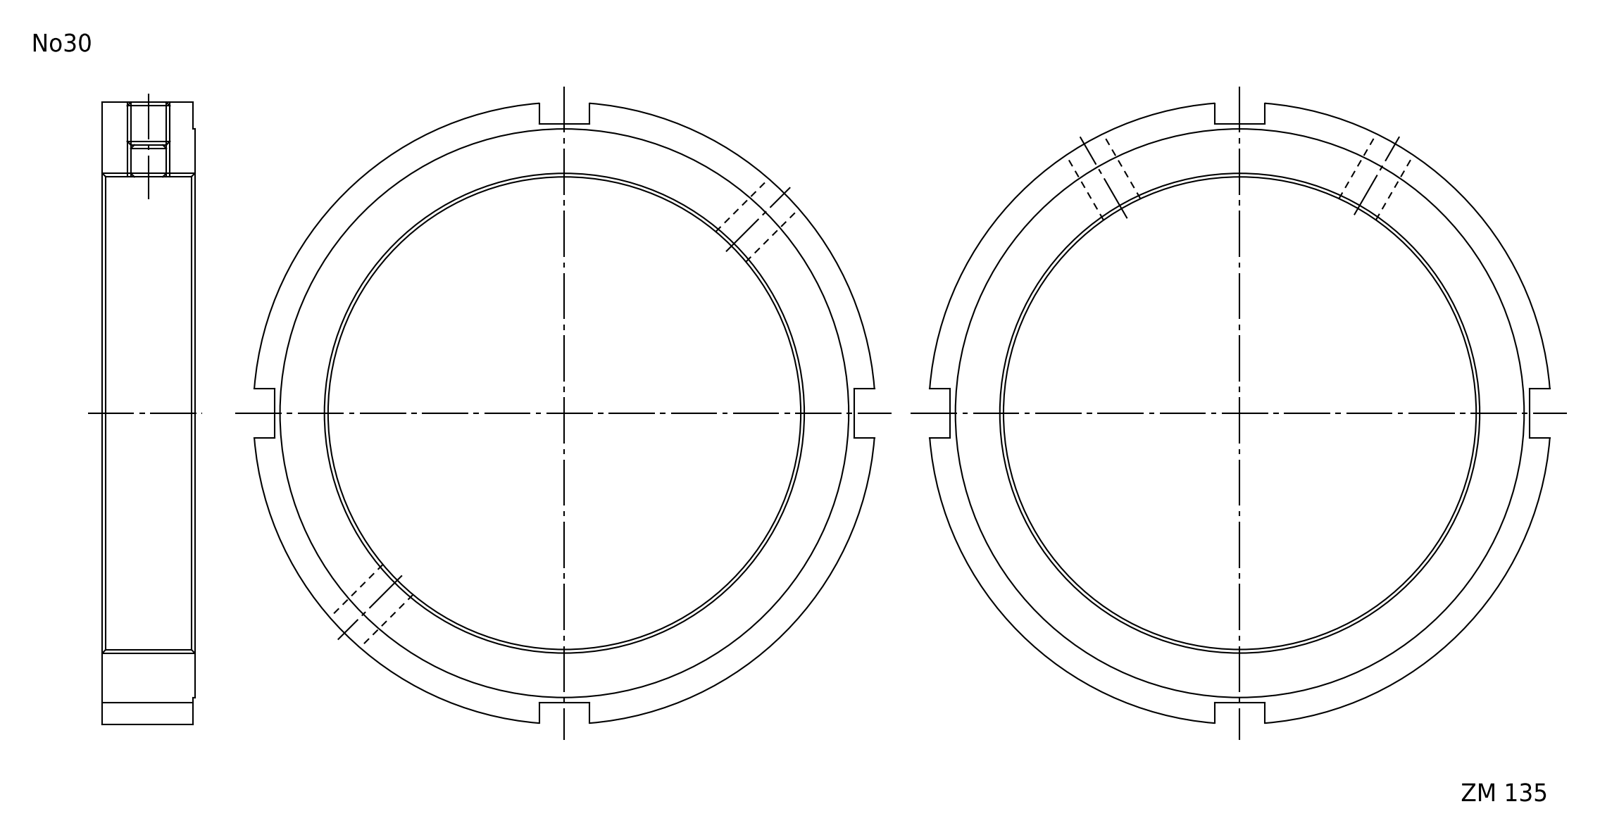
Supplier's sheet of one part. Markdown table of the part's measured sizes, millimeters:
| quantity | value |
| --- | --- |
| part name | FKD ZM135 |
| STEP written by | Autodesk Inventor 2011 (AUTOMOTIVE_DESIGN) |
| units | millimeters |
| bodies | 1 solid, 23 faces (15 planar, 8 cylindrical, 0 other) |
| overall size | 174.44 × 174.44 × 26 |
| volume | 239 595 mm³ |
| surface area | 46 230 mm² |
| round holes (diameter × count) | 10.11 × 2, 135 × 1 |
| round bosses / shafts (diameter × count) | 175 × 1, 160 × 1 |
| main face-to-face distances | 26, 0.5, 25.5, 74.5, 88.5, 163, 14 |
